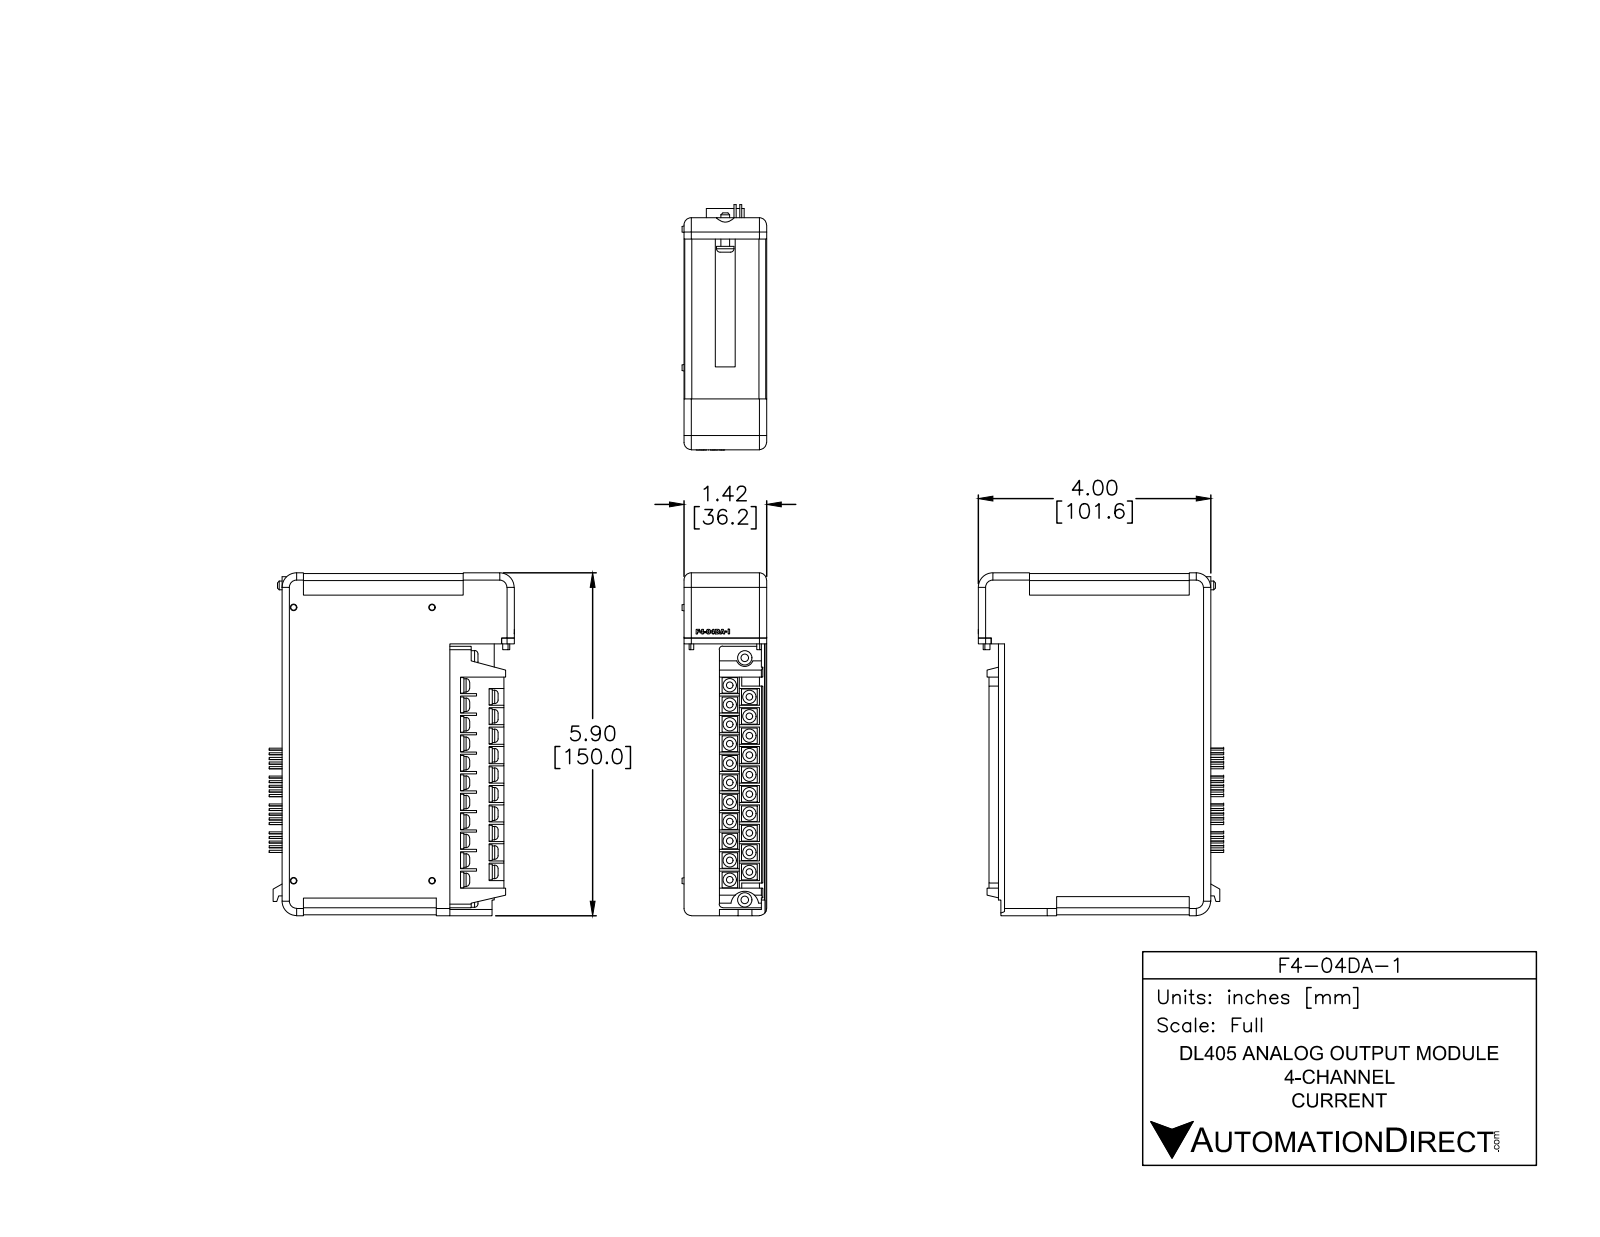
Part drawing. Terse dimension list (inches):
name: F4-04DA-1
written by: SolidWorks 2014 (AUTOMOTIVE_DESIGN)
unit: in
bodies: 6 solids, 894 faces (569 planar, 246 cylindrical, 79 other)
size: 5.905 × 4.223 × 1.455
volume: 27.6 in³; area: 90.48 in²
bosses: 21× ⌀0.23, 20× ⌀0.035, 20× ⌀0.035, 2× ⌀0.25, 1× ⌀0.3, 1× ⌀0.15
rounds: 82× R0.015, 8× R0.125, 4× R0.12, 3× R0.25, 2× R0.03, 2× R0.06, 1× R0.149, 1× R0.151
face distances: 1.425, 0.015, 2.89, 5.875, 1.41, 0.47, 0.955, 5.89, 1.21, 0.345
